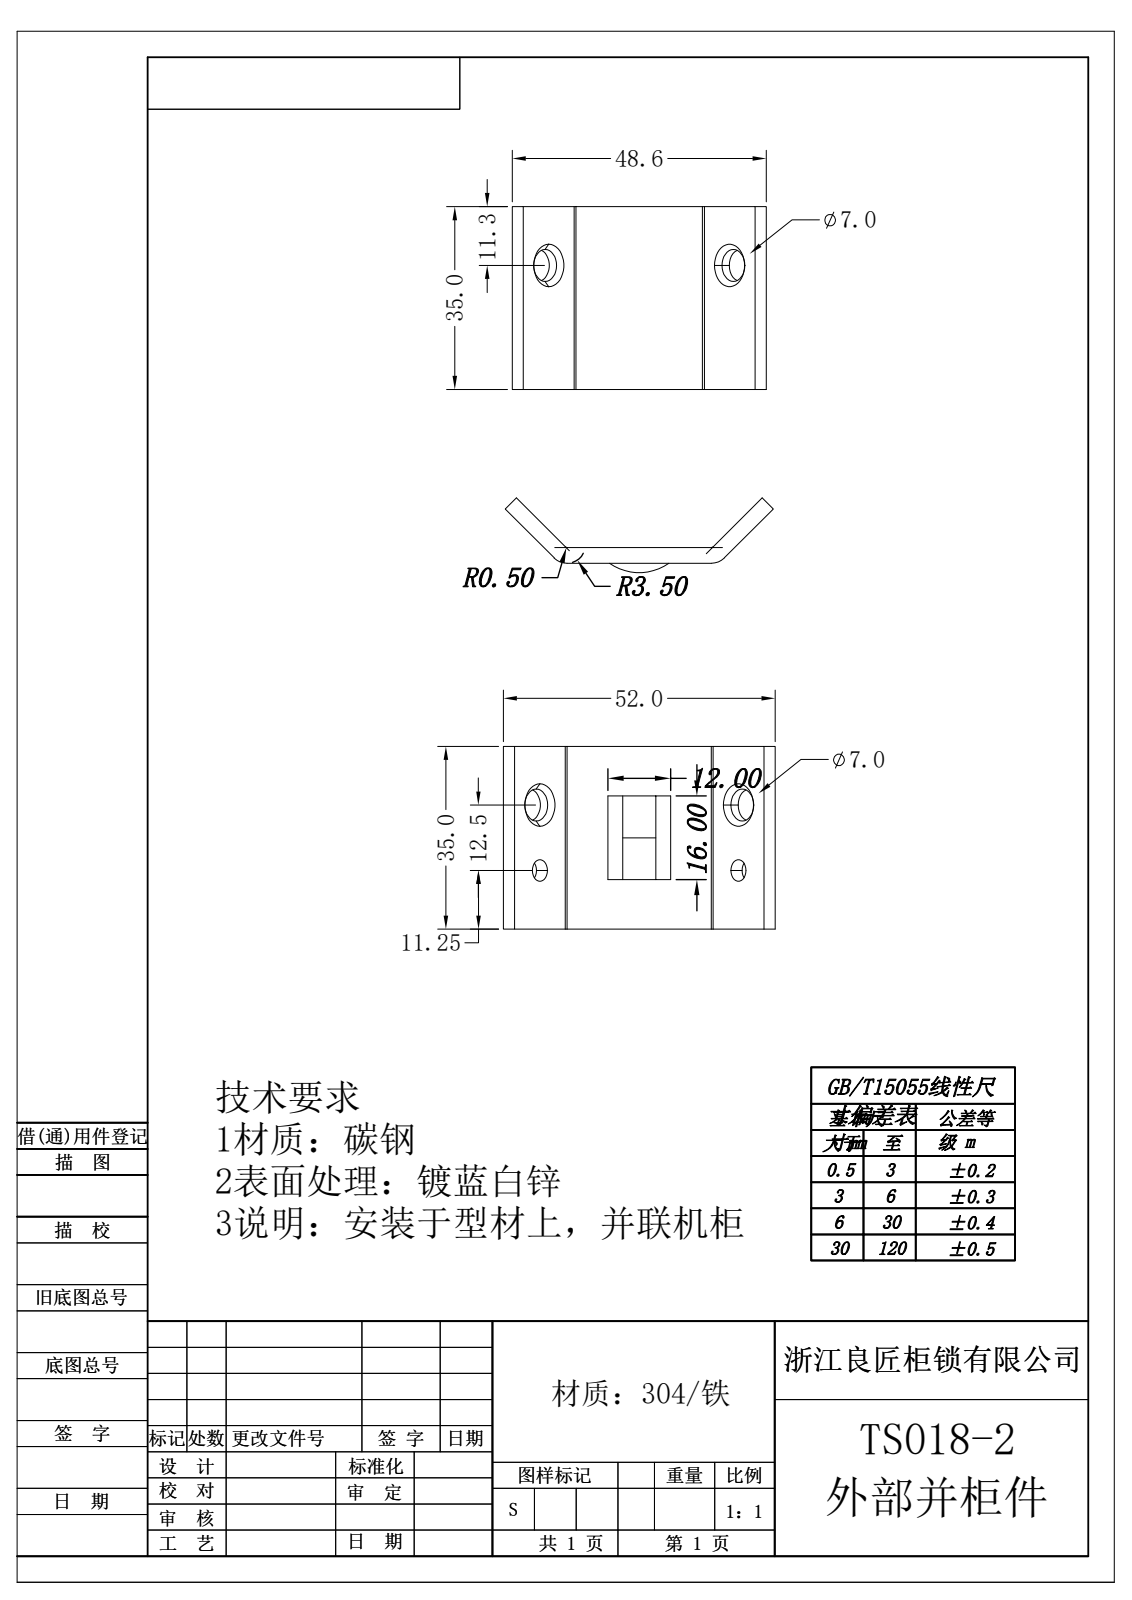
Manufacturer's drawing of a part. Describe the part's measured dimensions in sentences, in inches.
Its 3-D file was written by "Rhino 8.5 (CONFIG_CONTROL_DESIGN)". It is 1 solid with 80 faces: 20 planar, 40 cylindrical and 20 other. Overall it measures 2.019 by 1.378 by 0.532 inches. Its volume is 0.355 cubic inches and its surface area 7.242 square inches. Round holes: 2 of diameter 0.118, 2 of diameter 0.197. Partial cylindrical surfaces (rounded edges, fillets, slot ends): 24 of radius 0.01, 6 of radius 0.02, 2 of radius 0.138. The main face-to-face distances are 0.118, 0.039, 0.157, 0.079, 1.378, 1.309, 1.428, 1.427, 1.309, 0.013. The hole center spacings are 0.492.
